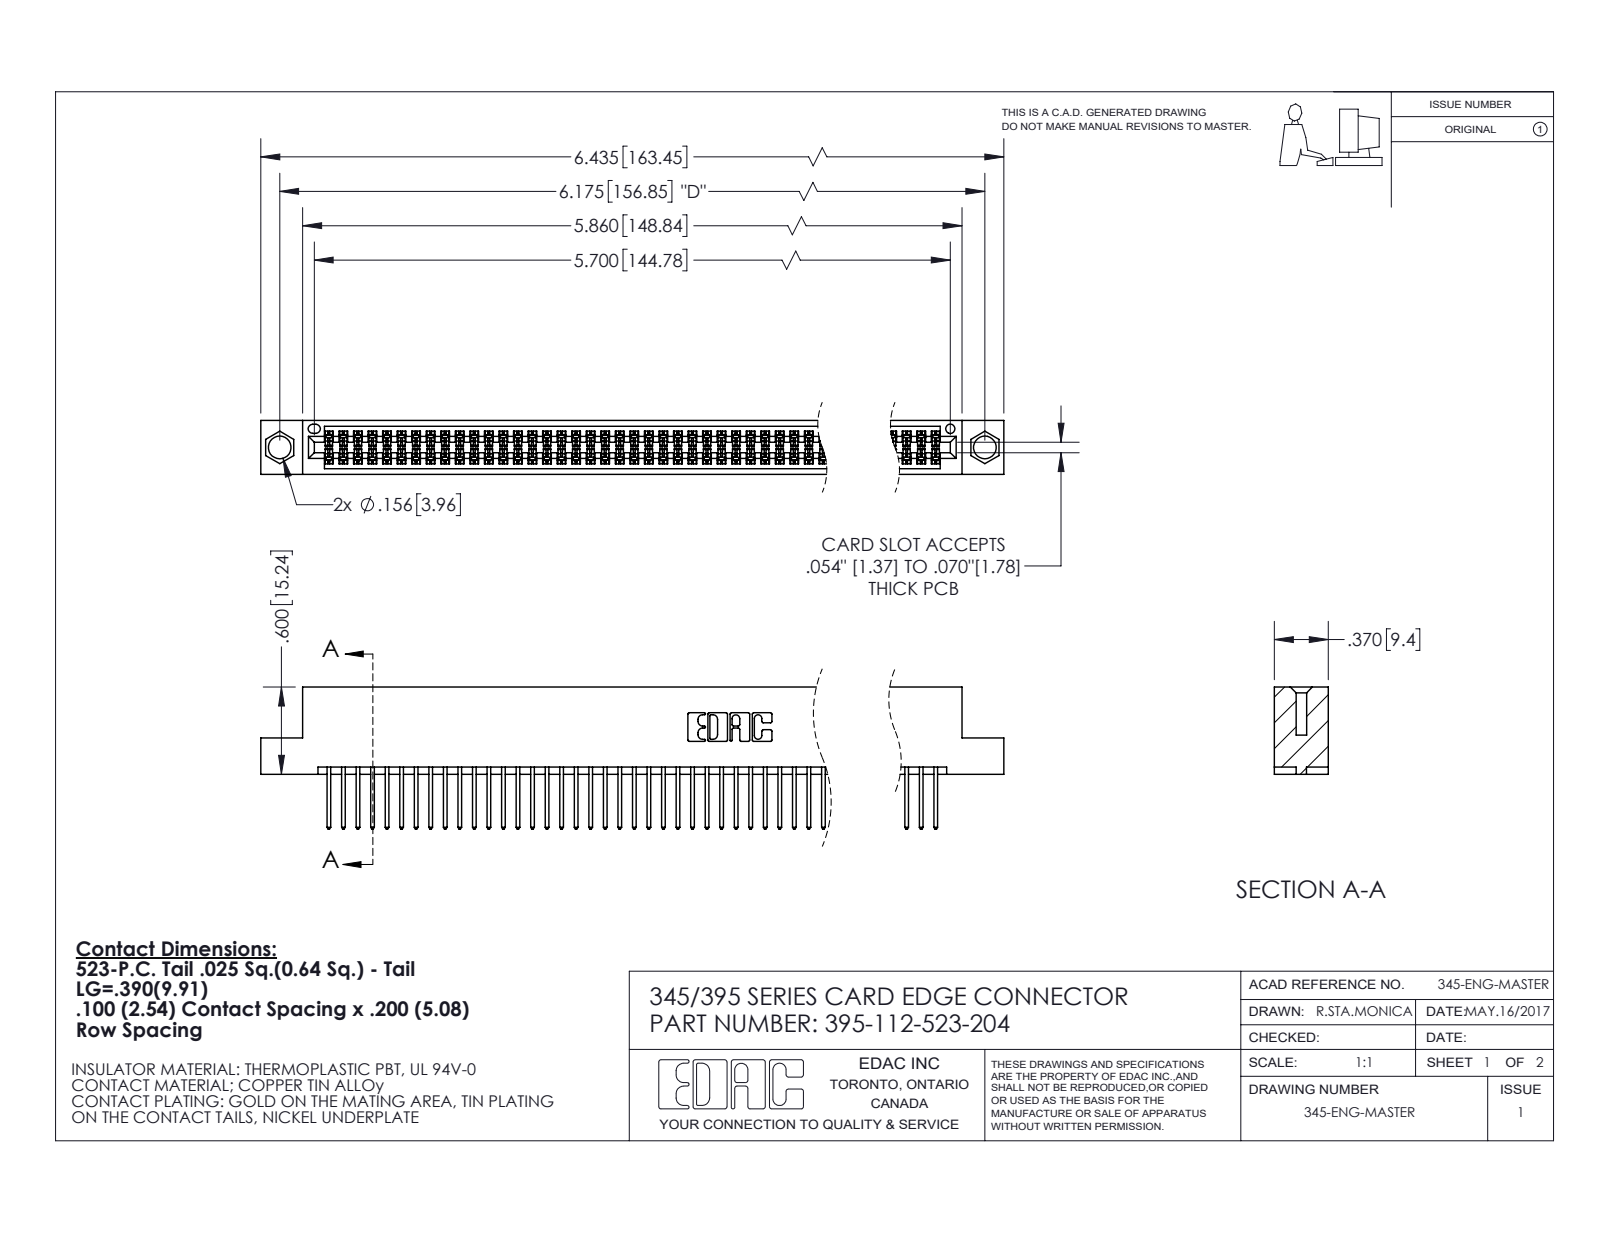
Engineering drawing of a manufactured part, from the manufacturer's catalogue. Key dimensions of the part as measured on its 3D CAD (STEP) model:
Part name (STEP PRODUCT): 345 Part_Flush Mounting Lugs - 0.156 Dia-TI; 345-292-001_345-293-123; 395-112-523-204
STEP written by: SolidWorks 2020 (CONFIG_CONTROL_DESIGN)
Units: inches
Bodies: 113 solids, 5740 faces (3790 planar, 1950 cylindrical, 0 other)
Overall size (bounding box): 6.435 × 0.977 × 0.37
Volume: 0.984 in³ · Surface area: 38.75 in²
Round holes (diameter × count): ⌀0.156 ×2, ⌀0.064 ×1
Partial cylindrical surfaces — rounded edges, fillets, slot ends (radius × count): R0.006 ×224, R0.01 ×112, R0.01 ×22, R0.007 ×6, R0.031 ×6, R0.026 ×3, R0.014 ×2, R0.019 ×2
Main face-to-face distances: 0.298, 0.072, 0.2, 0.098, 0.272, 0.025, 0.37, 0.225, 0.175, 0.149
Hole centre spacings: 0.27, 5.939, 6.175
